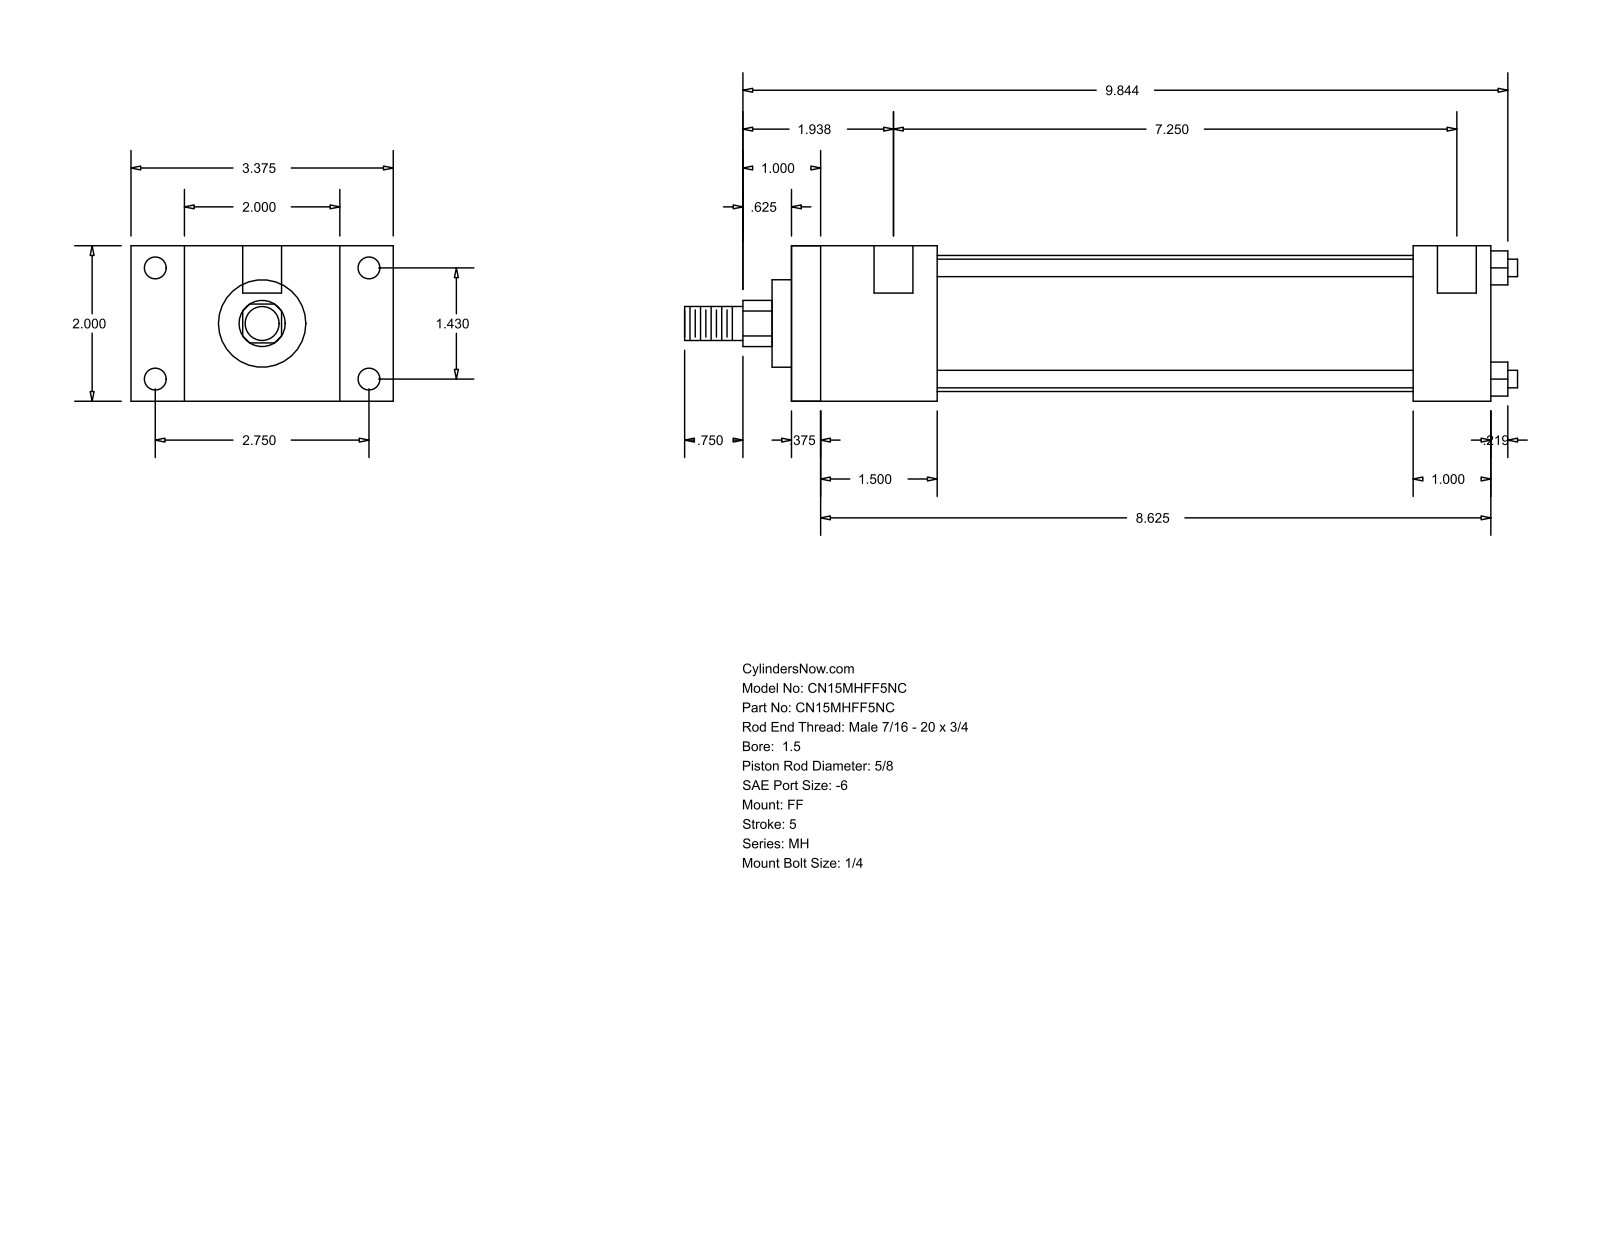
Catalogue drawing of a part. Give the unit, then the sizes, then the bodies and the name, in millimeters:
Units: millimetres
Overall size (bounding box): 272.26 × 85.72 × 50.8
Round holes (diameter × count): ⌀5.56 ×4, ⌀7.14 ×4, ⌀12.7 ×2
Round bosses / shafts (diameter × count): ⌀5.71 ×4, ⌀44.45 ×1, ⌀28.57 ×1, ⌀15.88 ×1, ⌀11.11 ×1
Partial cylindrical surfaces — rounded edges, fillets, slot ends (radius × count): R7.54 ×1
Main face-to-face distances: 50.8, 228.59, 219.07, 9.52, 25.4, 17.46, 68.26, 47.62, 38.1, 180.97
Hole centre spacings: 36.32, 69.84, 78.72, 187.32, 3.17, 184.15
Bodies: 0 solids, 92 faces (64 planar, 28 cylindrical, 0 other)
Part name (STEP PRODUCT): MH_FF__0150_0.625
STEP written by: GSSL Pune (CONFIG_CONTROL_DESIGN)
